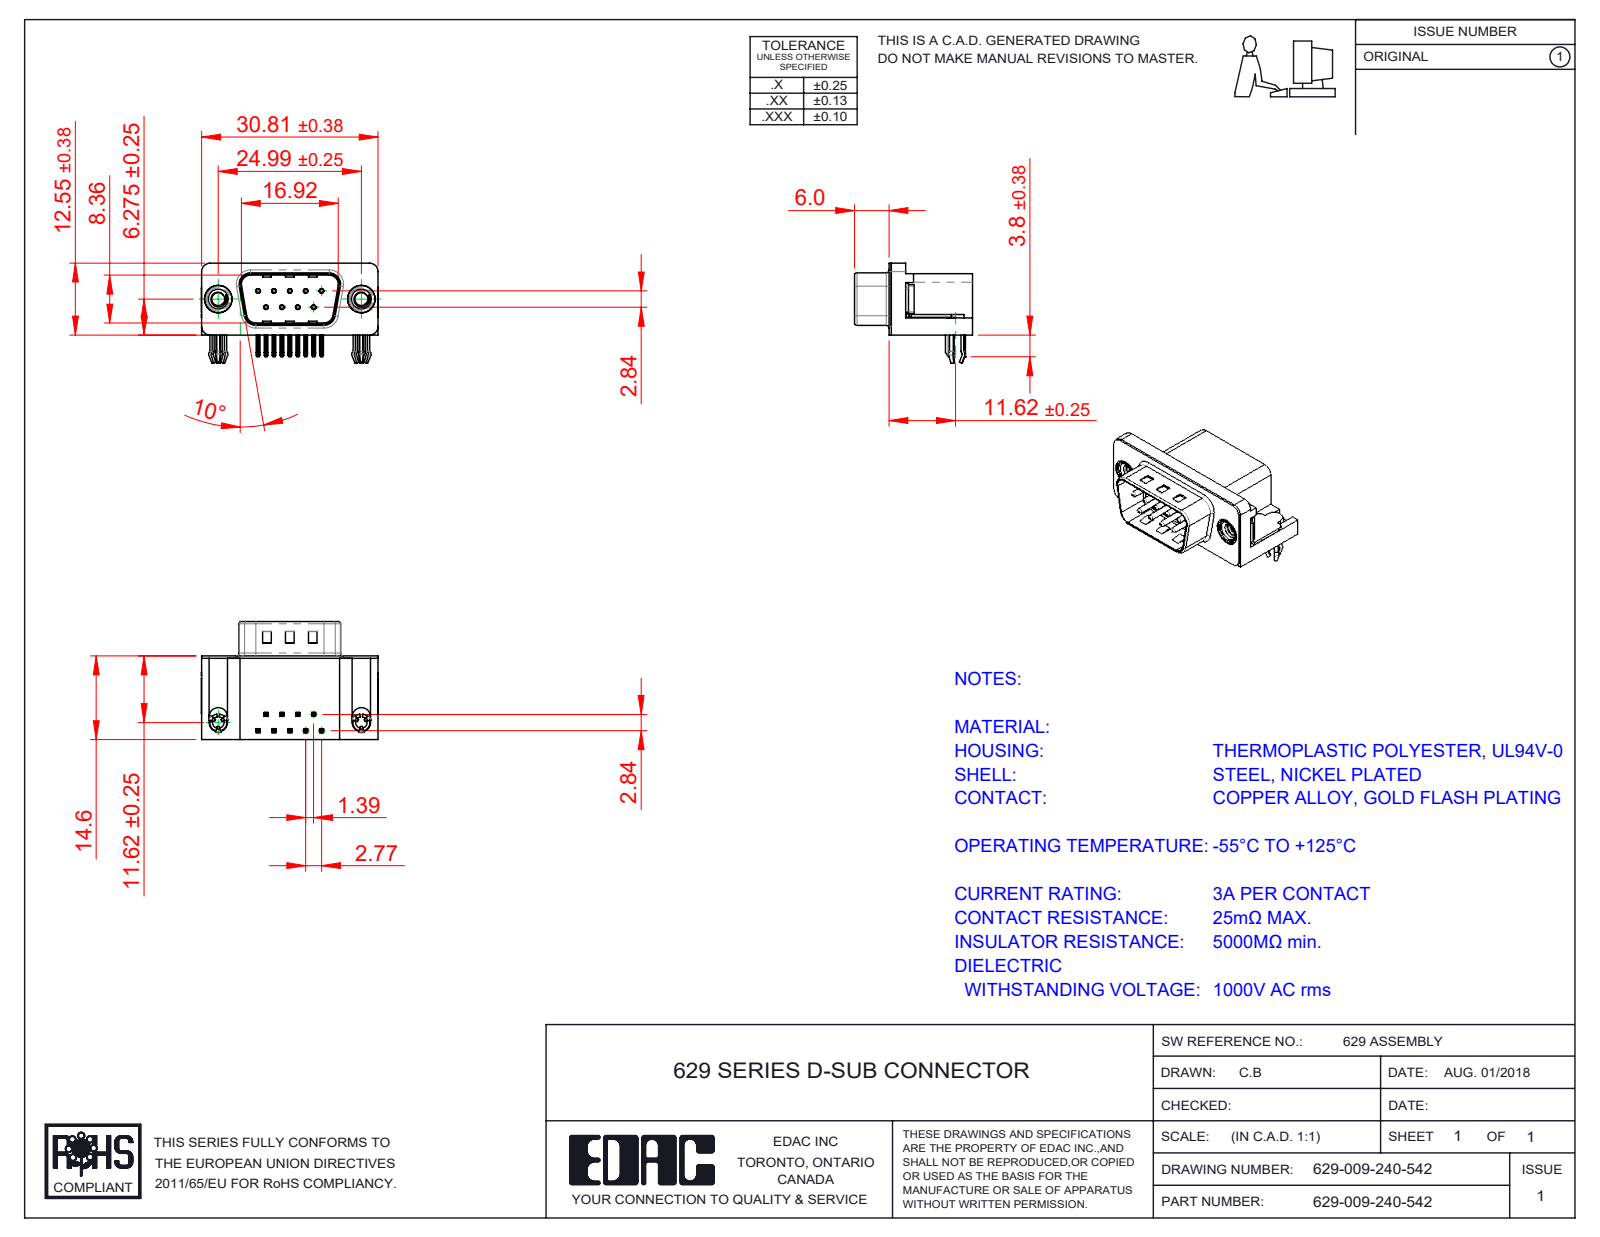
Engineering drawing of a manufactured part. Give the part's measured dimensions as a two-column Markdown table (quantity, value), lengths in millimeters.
| quantity | value |
| --- | --- |
| part name | 629 Contact Bottom; 629 Shell_09 Socket; 629 3 Prong Board Lock; 629-009-240-542 (+3 more) |
| STEP written by | SolidWorks 2020 (CONFIG_CONTROL_DESIGN) |
| units | millimeters |
| bodies | 15 solids, 1093 faces (609 planar, 321 cylindrical, 163 other) |
| overall size | 30.89 × 20.6 × 17.48 |
| volume | 3 731 mm³ |
| surface area | 4 819 mm² |
| round holes (diameter × count) | 0.35 × 9, 0.8 × 9, 2 × 2, 2.26 × 2, 4 × 2, 4.8 × 2, 5 × 2 |
| round bosses / shafts (diameter × count) | 0.75 × 9, 4.9 × 2, 4.75 × 2, 3.9 × 2, 3 × 2 |
| partial cylindrical surfaces (radius × count) | 0.25 × 48, 0.12 × 18, 1 × 16, 0.5 × 9, 1.5 × 8, 1.6 × 8, 0.9 × 4, 2 × 4 |
| main face-to-face distances | 0.4, 14.2, 10.35, 14.6, 0.5, 2.9, 11.7, 2.5, 2.1, 6.7 |
| hole center spacings | 3.16, 2.77, 5.54, 5.03, 5.04, 8.31, 7.48, 7.49 |
